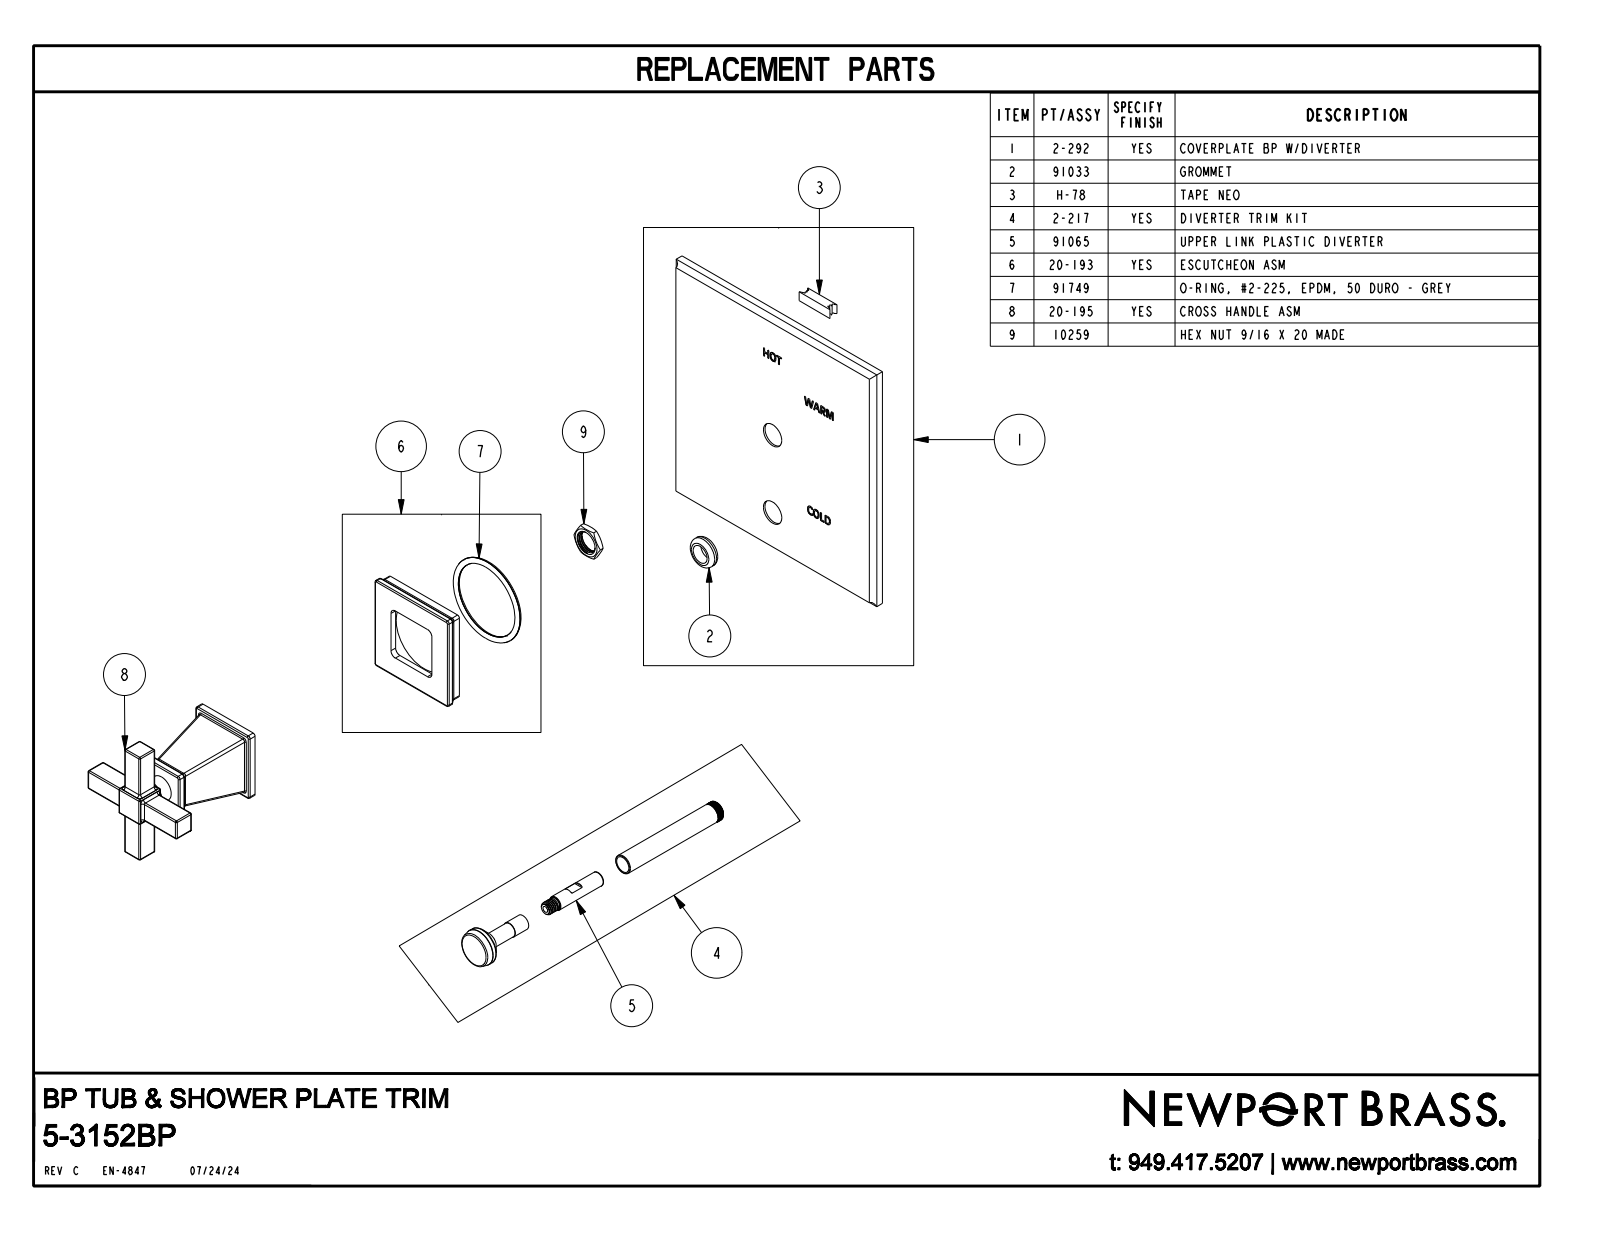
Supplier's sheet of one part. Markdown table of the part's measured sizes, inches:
| quantity | value |
| --- | --- |
| part name | 5-3152BP |
| STEP written by | CREO PARAMETRIC BY PTC INC, 2018400 (CONFIG_CONTROL_DESIGN) |
| units | inches |
| bodies | 1 solid, 484 faces (164 planar, 132 cylindrical, 188 other) |
| overall size | 6.5 × 6.5 × 3.941 |
| volume | 20.37 in³ |
| surface area | 120.4 in² |
| round bosses / shafts (diameter × count) | 0.9 × 1, 0.625 × 1, 0.506 × 1, 0.354 × 1 |
| partial cylindrical surfaces (radius × count) | 0.03 × 60, 0.06 × 36, 0.09 × 8, 0.125 × 4, 0.23 × 4 |
| main face-to-face distances | 0.313, 0.5, 3, 3.5, 0.723, 0.41, 6.5, 3.348, 3.848, 3.035 |
